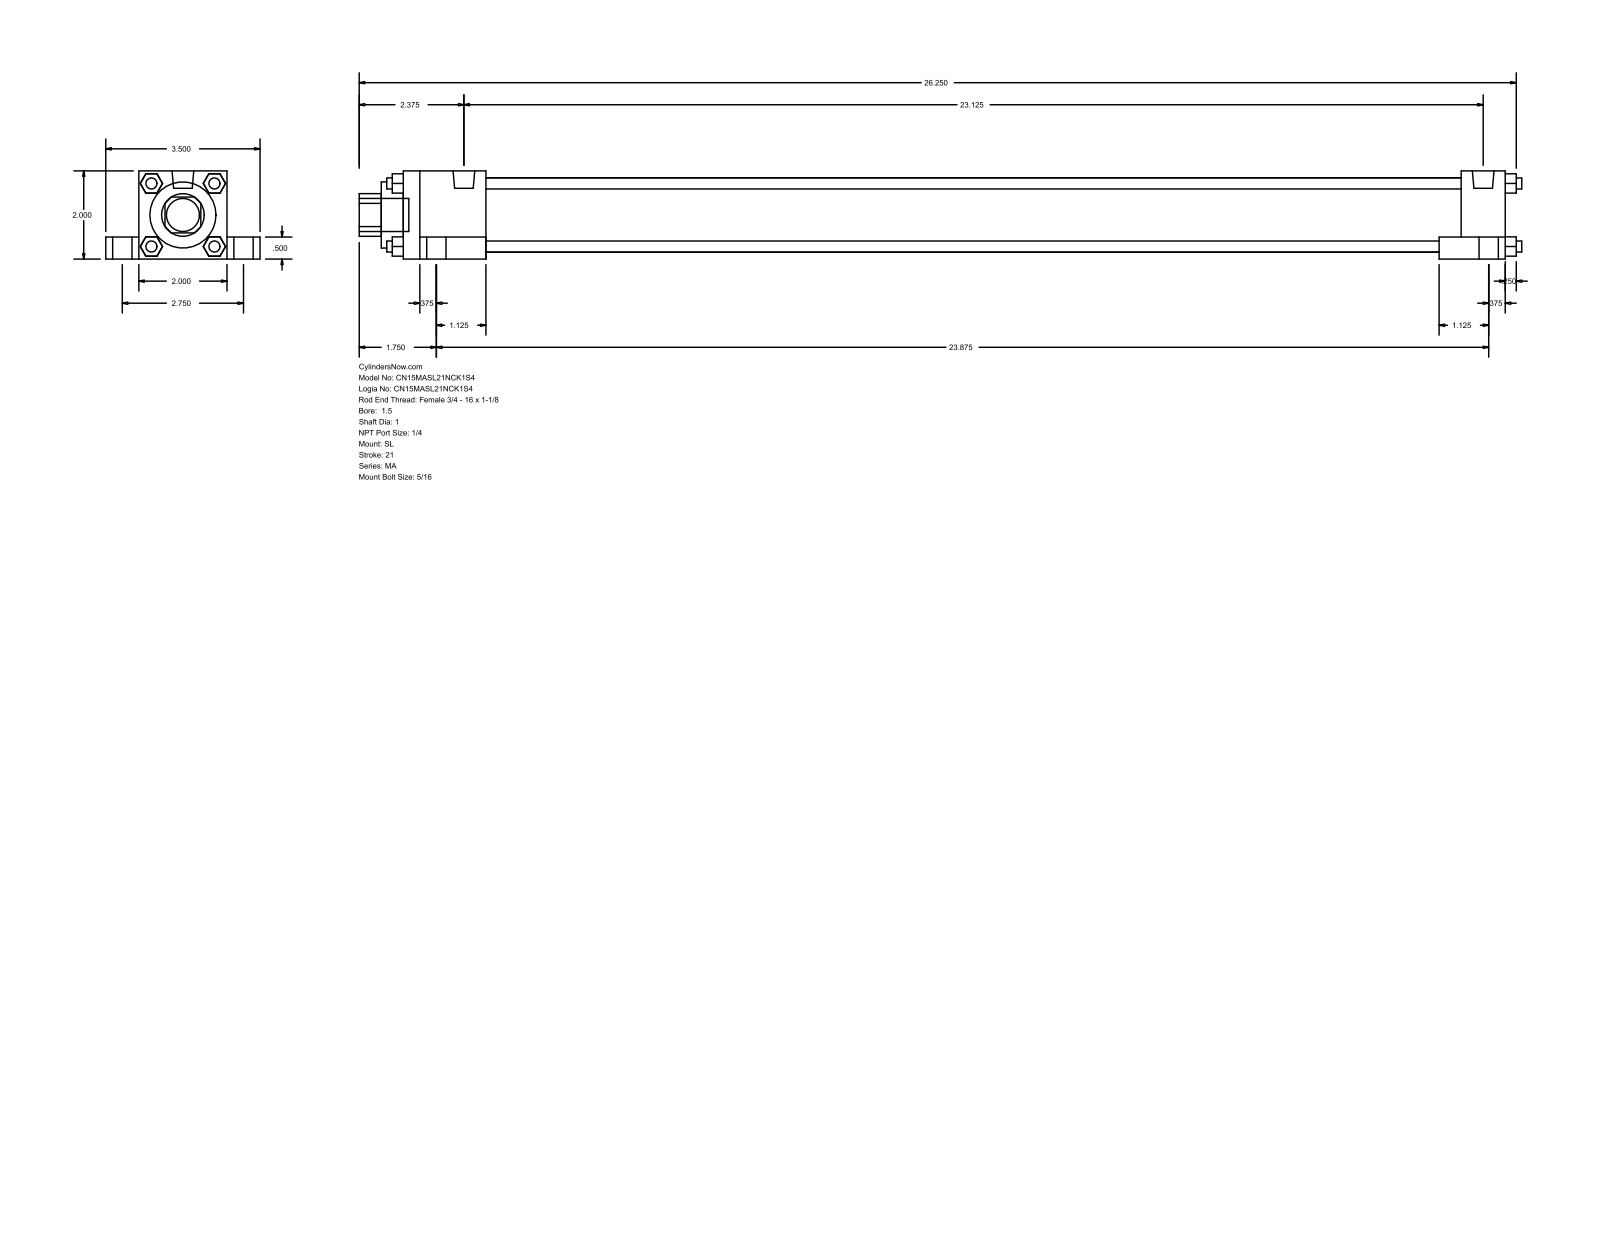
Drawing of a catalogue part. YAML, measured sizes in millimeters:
part_name: "MA_SL__0150_1"
step_written_by: "GSSL Pune (CONFIG_CONTROL_DESIGN)"
units: millimeters
bodies: {solids: 0, faces: 148, planar: 112, cylindrical: 36, other: 0}
overall_size: [669.92, 88.9, 50.8]
round_holes:
  - {diameter: 25.4, count: 1}
  - {diameter: 38.1, count: 1}
  - {diameter: 42.93, count: 1}
round_bosses_or_shafts:
  - {diameter: 17.46, count: 4}
  - {diameter: 11.11, count: 4}
  - {diameter: 7.94, count: 4}
  - {diameter: 6.35, count: 4}
  - {diameter: 12.49, count: 2}
  - {diameter: 19.05, count: 1}
partial_cylinders:
  - {radius: 12.29, count: 1}
face_to_face_distances: [50.8, 12.7, 19.05, 9.52, 69.85, 38.1, 6.35, 635, 25.4, 609.6]
